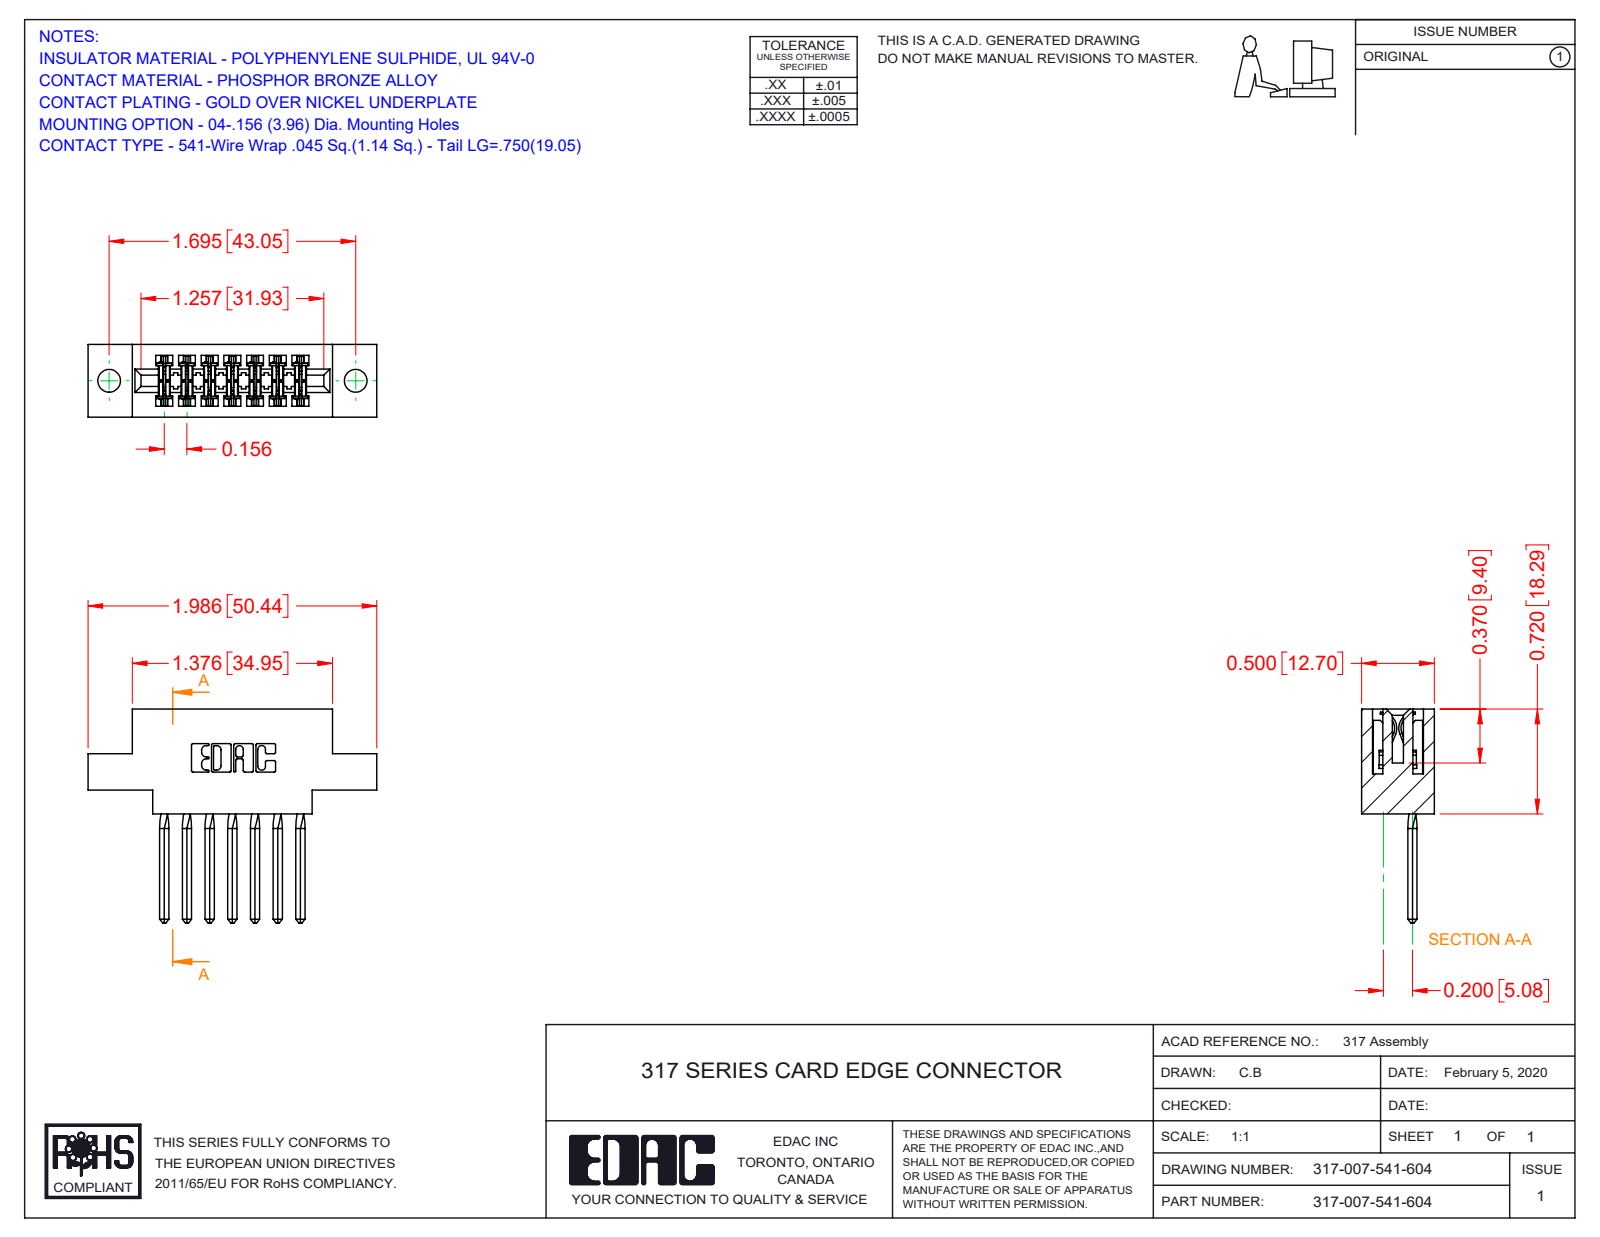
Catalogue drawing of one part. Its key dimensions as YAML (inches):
part_name: "317-007-541-604; 317-290-002_541; 317 Part_.156 Dia - TH"
step_written_by: "SolidWorks 2016 (CONFIG_CONTROL_DESIGN)"
units: inches
bodies: {solids: 8, faces: 1166, planar: 926, cylindrical: 212, other: 28}
overall_size: [1.986, 1.47, 0.5]
volume: 0.428
surface_area: 13.28
round_holes:
  - {diameter: 0.156, count: 2}
partial_cylinders:
  - {radius: 0.01, count: 22}
  - {radius: 0.015, count: 14}
  - {radius: 0.007, count: 6}
  - {radius: 0.031, count: 6}
  - {radius: 0.026, count: 3}
  - {radius: 0.095, count: 2}
  - {radius: 0.1, count: 2}
  - {radius: 0.11, count: 2}
face_to_face_distances: [0.5, 0.075, 0.425, 0.11, 0.156, 0.065, 0.22, 0.116, 0.163, 0.312]
hole_center_spacings: [1.695]
